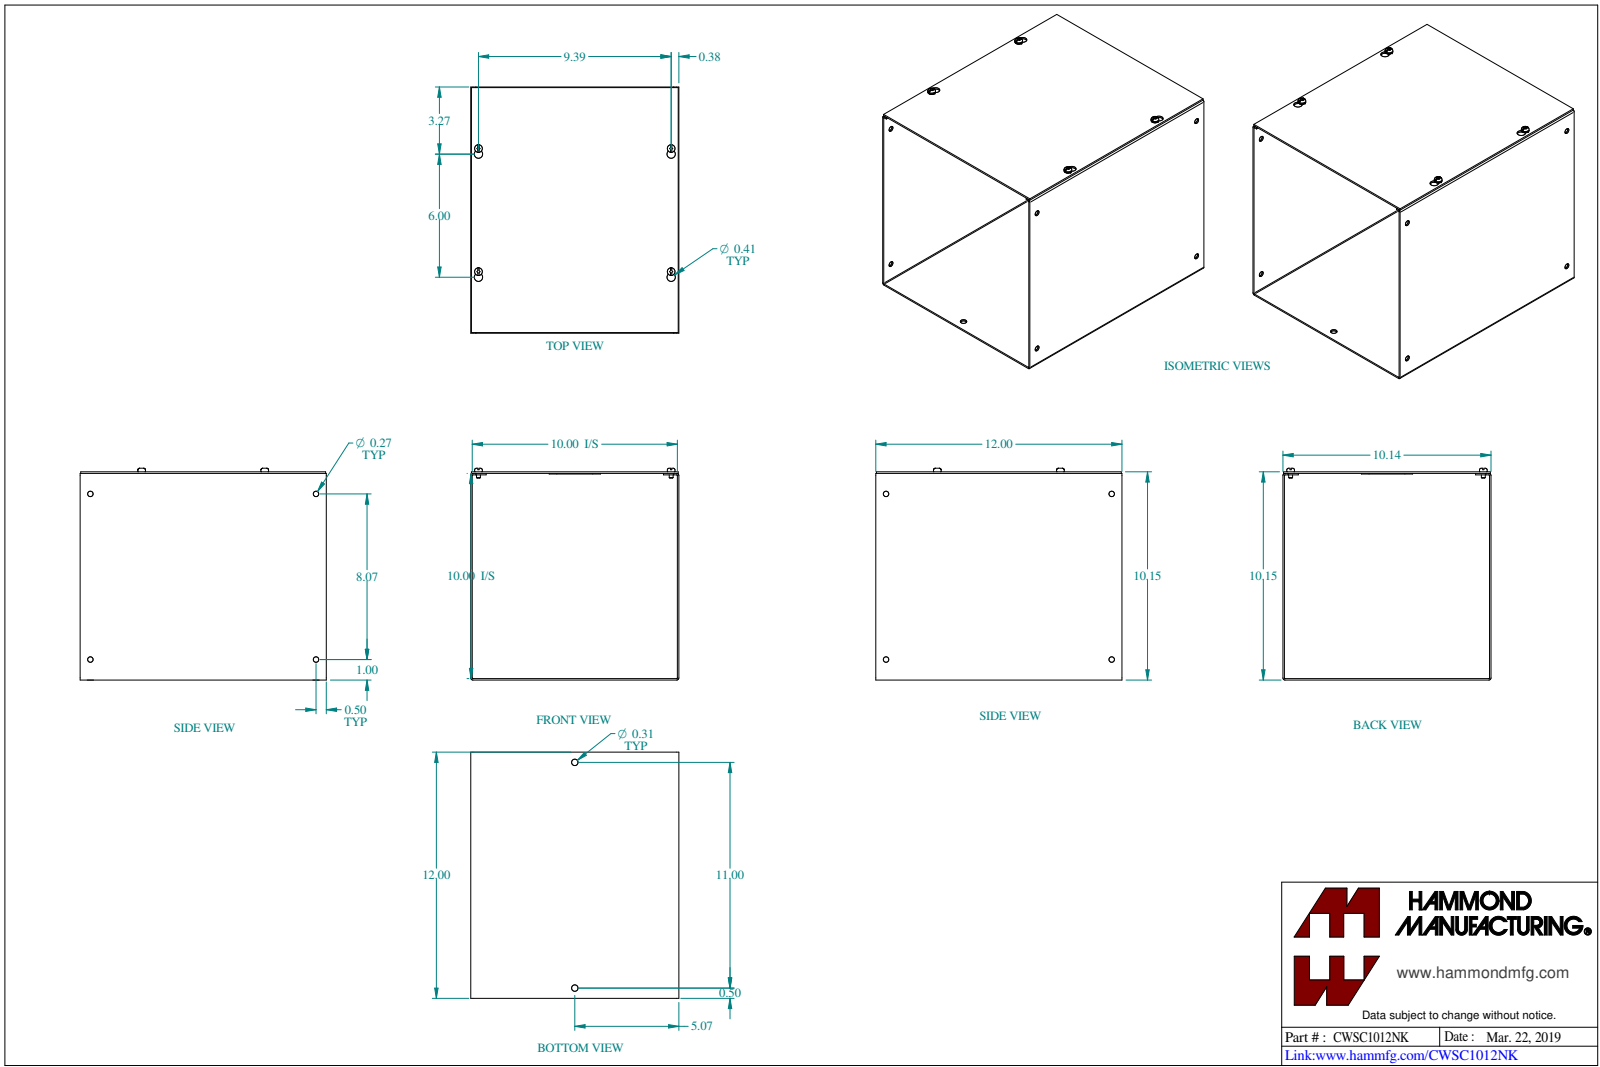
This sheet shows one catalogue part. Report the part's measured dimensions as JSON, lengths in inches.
{"part_name": "CWSC1012NK", "step_written_by": "SolidWorks 2023 (CONFIG_CONTROL_DESIGN)", "units": "inches", "bodies": {"solids": 6, "faces": 180, "planar": 88, "cylindrical": 68, "other": 24}, "overall_size": [12, 10.325, 10.144], "volume_in3": 36.34, "surface_area_in2": 1000, "round_holes": [[0.177, 4], [0.266, 4], [0.313, 2]], "round_bosses_or_shafts": [[0.375, 4], [0.19, 4]], "partial_cylinders_radius": [[0.036, 4], [0.108, 4], [0.125, 4], [0.203, 4]], "face_to_face_distances": [0.072, 10.072, 10, 0.078, 10.15, 10.078, 10.144, 9.928, 0.15, 0.031], "hole_center_spacings": [5.321, 9.711, 11, 6, 8.072, 9.394, 11.146, 13.644]}
